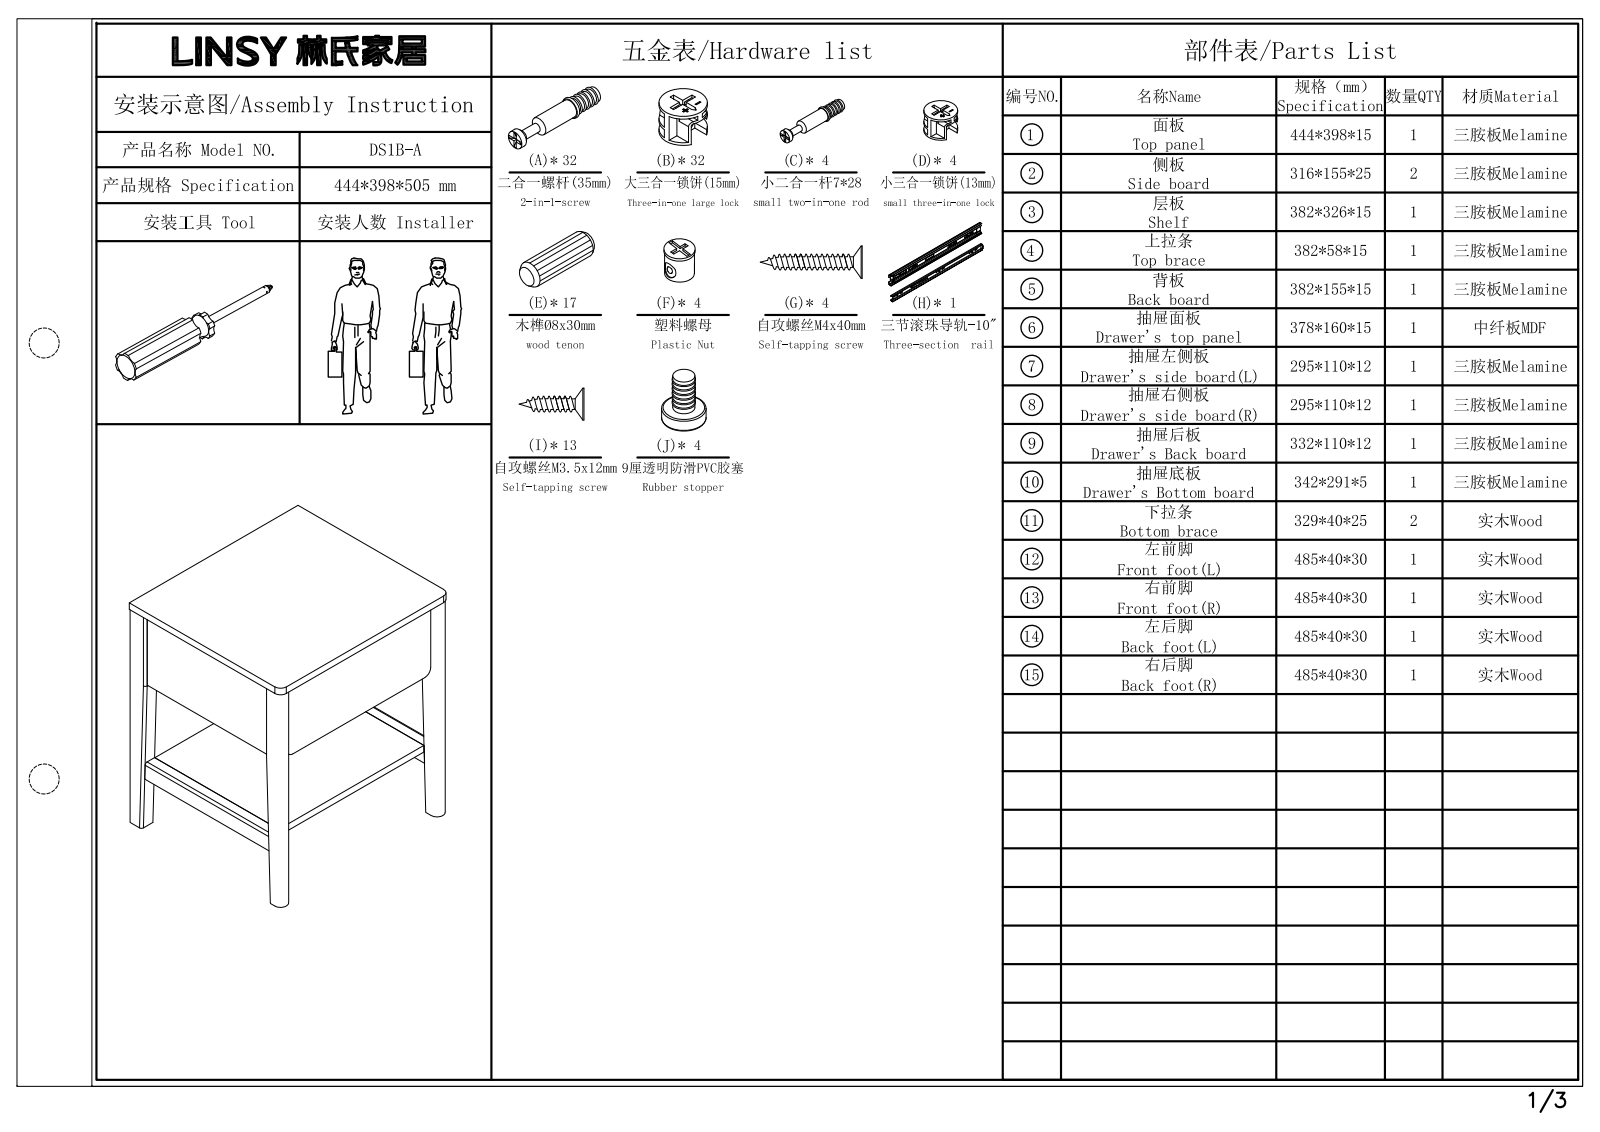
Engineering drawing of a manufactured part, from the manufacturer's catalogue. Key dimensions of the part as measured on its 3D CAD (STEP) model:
STEP written by: ACIS (automotive_design)
Units: millimetres
Bodies: 2 solids, 35 faces (9 planar, 16 cylindrical, 10 other)
Overall size (bounding box): 115 × 22 × 22
Volume: 31 786 mm³ · Surface area: 11 835 mm²
Round holes (diameter × count): ⌀17.36 ×1
Round bosses / shafts (diameter × count): ⌀22 ×1, ⌀17 ×1
Partial cylindrical surfaces — rounded edges, fillets, slot ends (radius × count): R1.22 ×1, R2.01 ×1, R2.77 ×1, R8.49 ×1
Main face-to-face distances: 38, 115, 77, 0.78, 83.84, 45.84, 31.16
